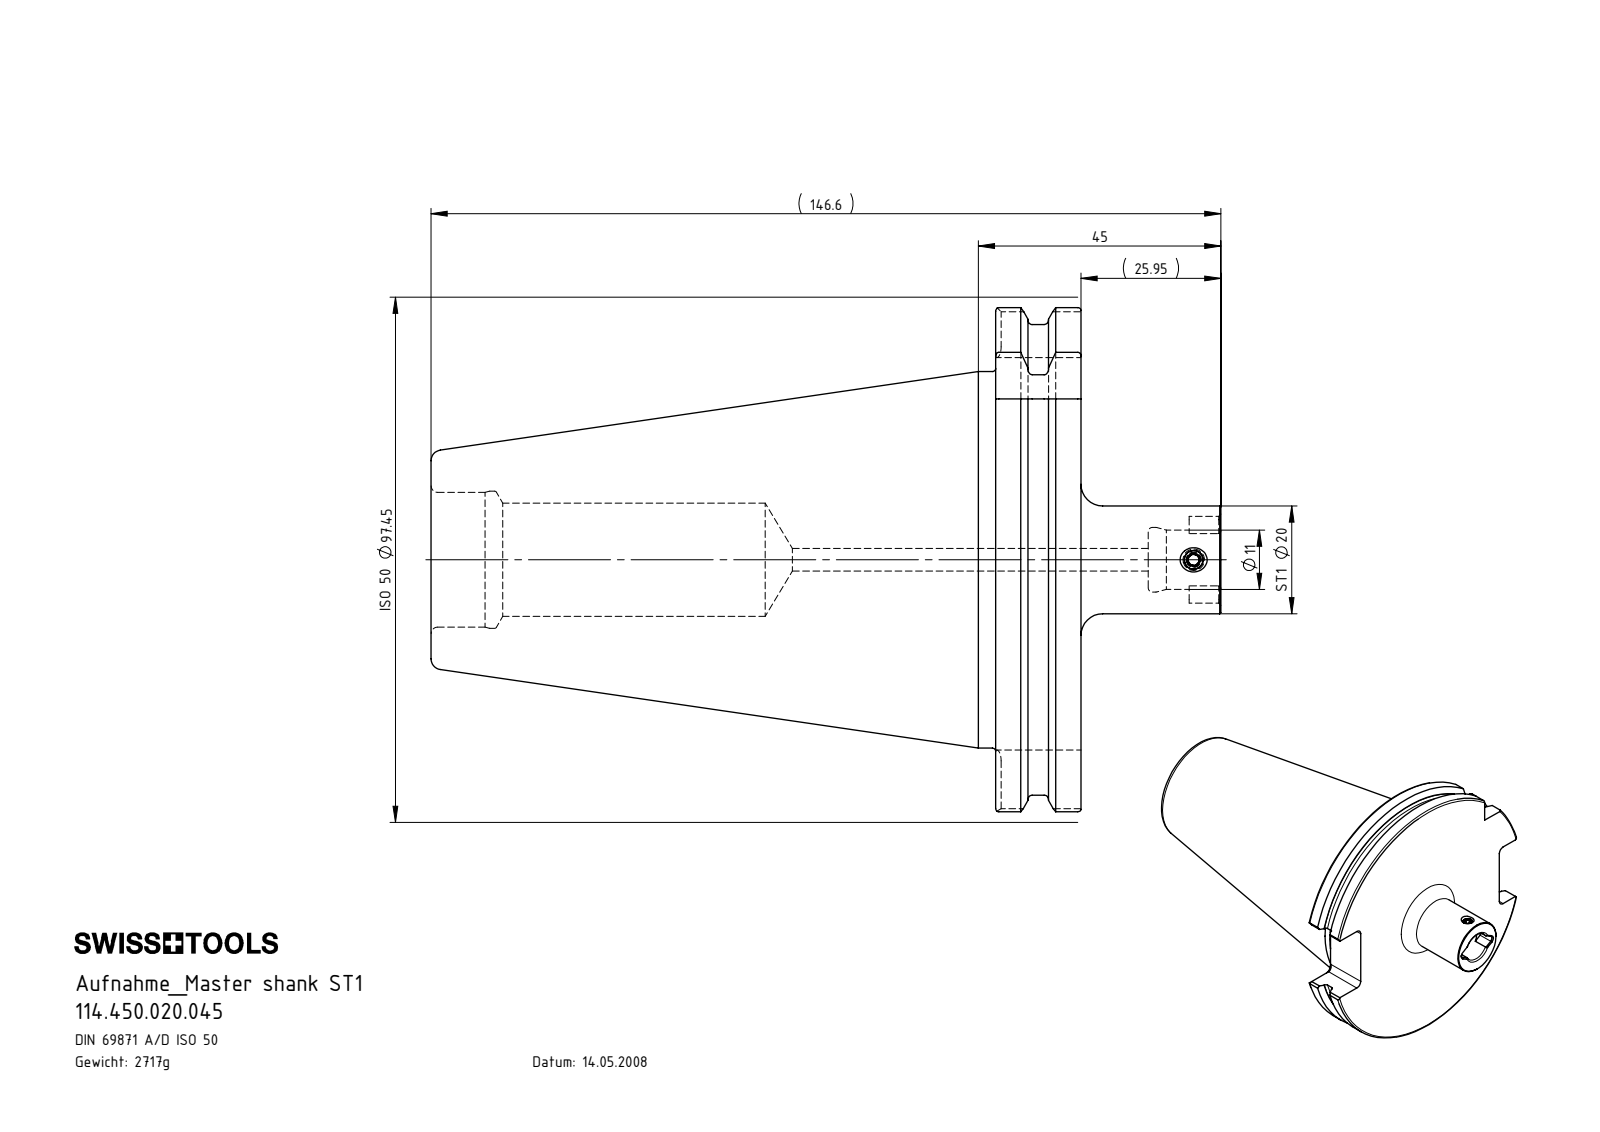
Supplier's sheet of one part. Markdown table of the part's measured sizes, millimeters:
| quantity | value |
| --- | --- |
| part name | SK5.ST1.K01.045; ST1-ER1.001.005_A; SK5-ST1.K01.045_B |
| STEP written by | SolidWorks 2017 (AUTOMOTIVE_DESIGN) |
| units | millimeters |
| bodies | 2 solids, 126 faces (54 planar, 30 cylindrical, 42 other) |
| overall size | 146.6 × 97.45 × 93.51 |
| volume | 346 113 mm³ |
| surface area | 42 698 mm² |
| round holes (diameter × count) | 2 × 1, 3.5 × 1, 4.2 × 1, 11 × 1, 12 × 1, 21 × 1, 25 × 1, 25.45 × 1 |
| round bosses / shafts (diameter × count) | 91 × 1, 69.85 × 1, 20 × 1, 4 × 1 |
| partial cylindrical surfaces (radius × count) | 2 × 8, 1.3 × 2, 48.73 × 1 |
| main face-to-face distances | 15.85, 104.8, 120.65, 72.8, 25.7, 146.6, 41.8, 25.95, 42.7, 17 |
